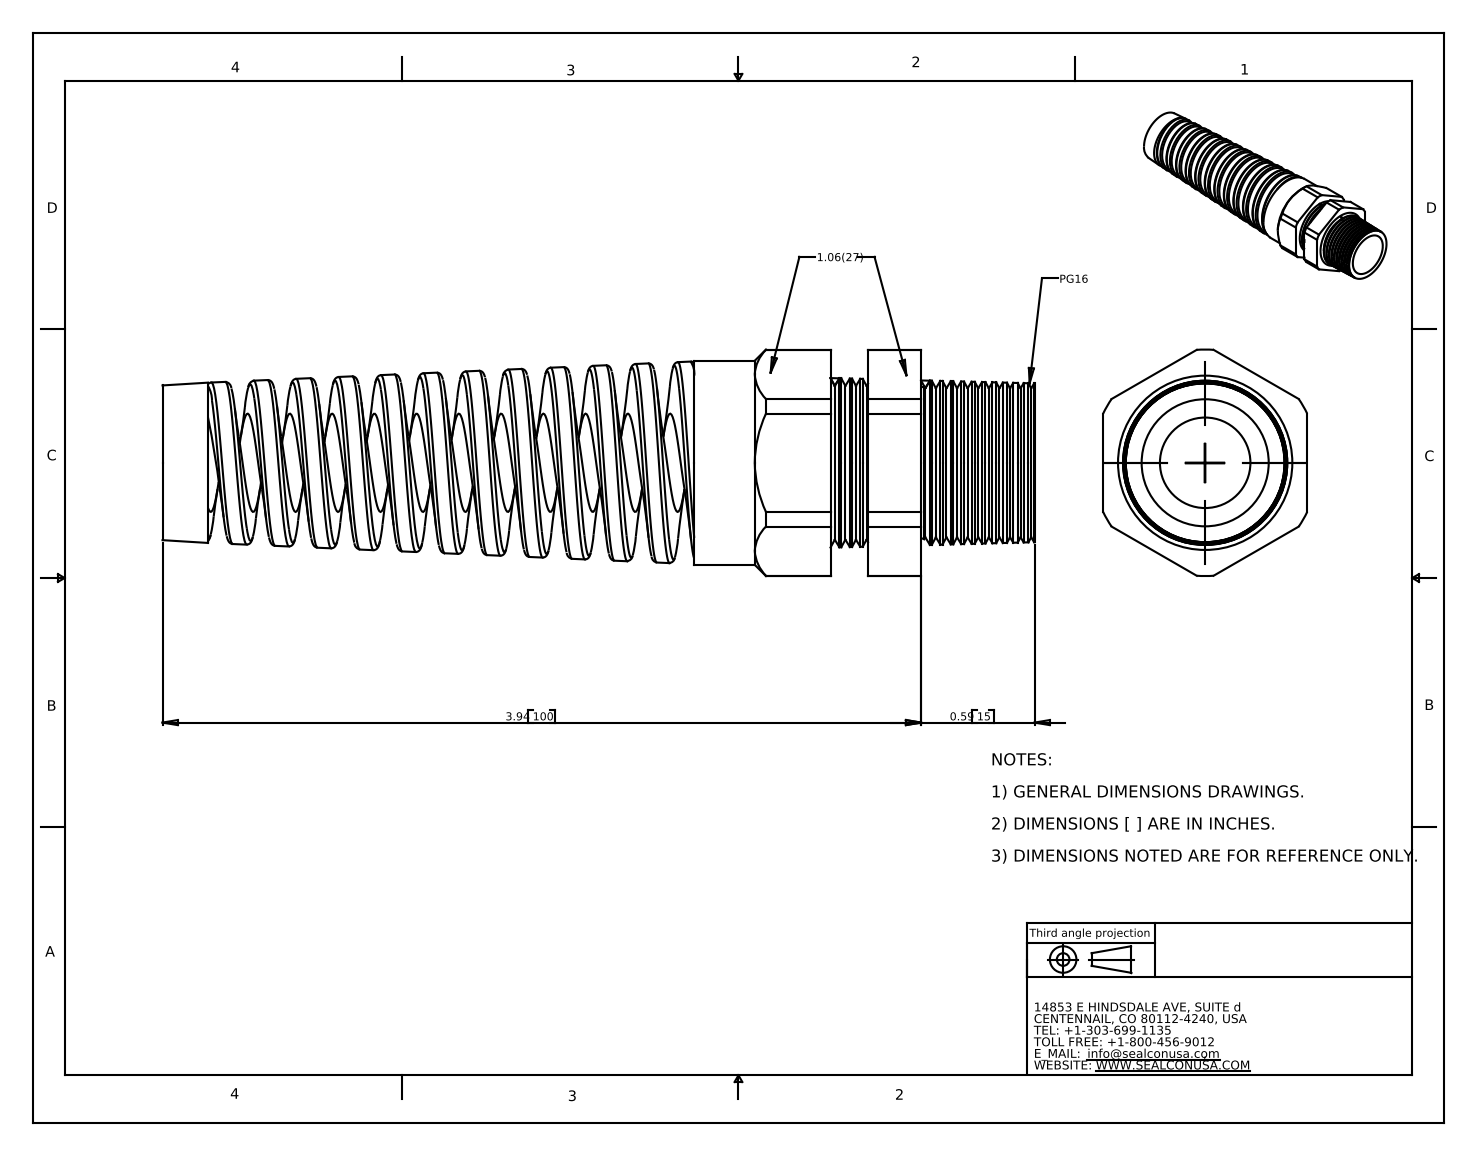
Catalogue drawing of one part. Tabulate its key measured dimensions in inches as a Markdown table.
| quantity | value |
| --- | --- |
| part name | CF16CR-GY |
| STEP written by | SolidWorks 2007 (CONFIG_CONTROL_DESIGN) |
| units | inches |
| bodies | 2 solids, 210 faces (24 planar, 49 cylindrical, 137 other) |
| overall size | 4.53 × 1.177 × 1.06 |
| volume | 1.749 in³ |
| surface area | 31.69 in² |
| round holes (diameter × count) | 0.47 × 1, 0.511 × 1, 0.54 × 1 |
| round bosses / shafts (diameter × count) | 1.06 × 1, 0.66 × 1 |
| partial cylindrical surfaces (radius × count) | 0.588 × 1 |
| main face-to-face distances | 1.06, 0.194, 0.47, 0.276, 0.708, 0.902, 1.178, 2.762, 3.47, 3.665 |
